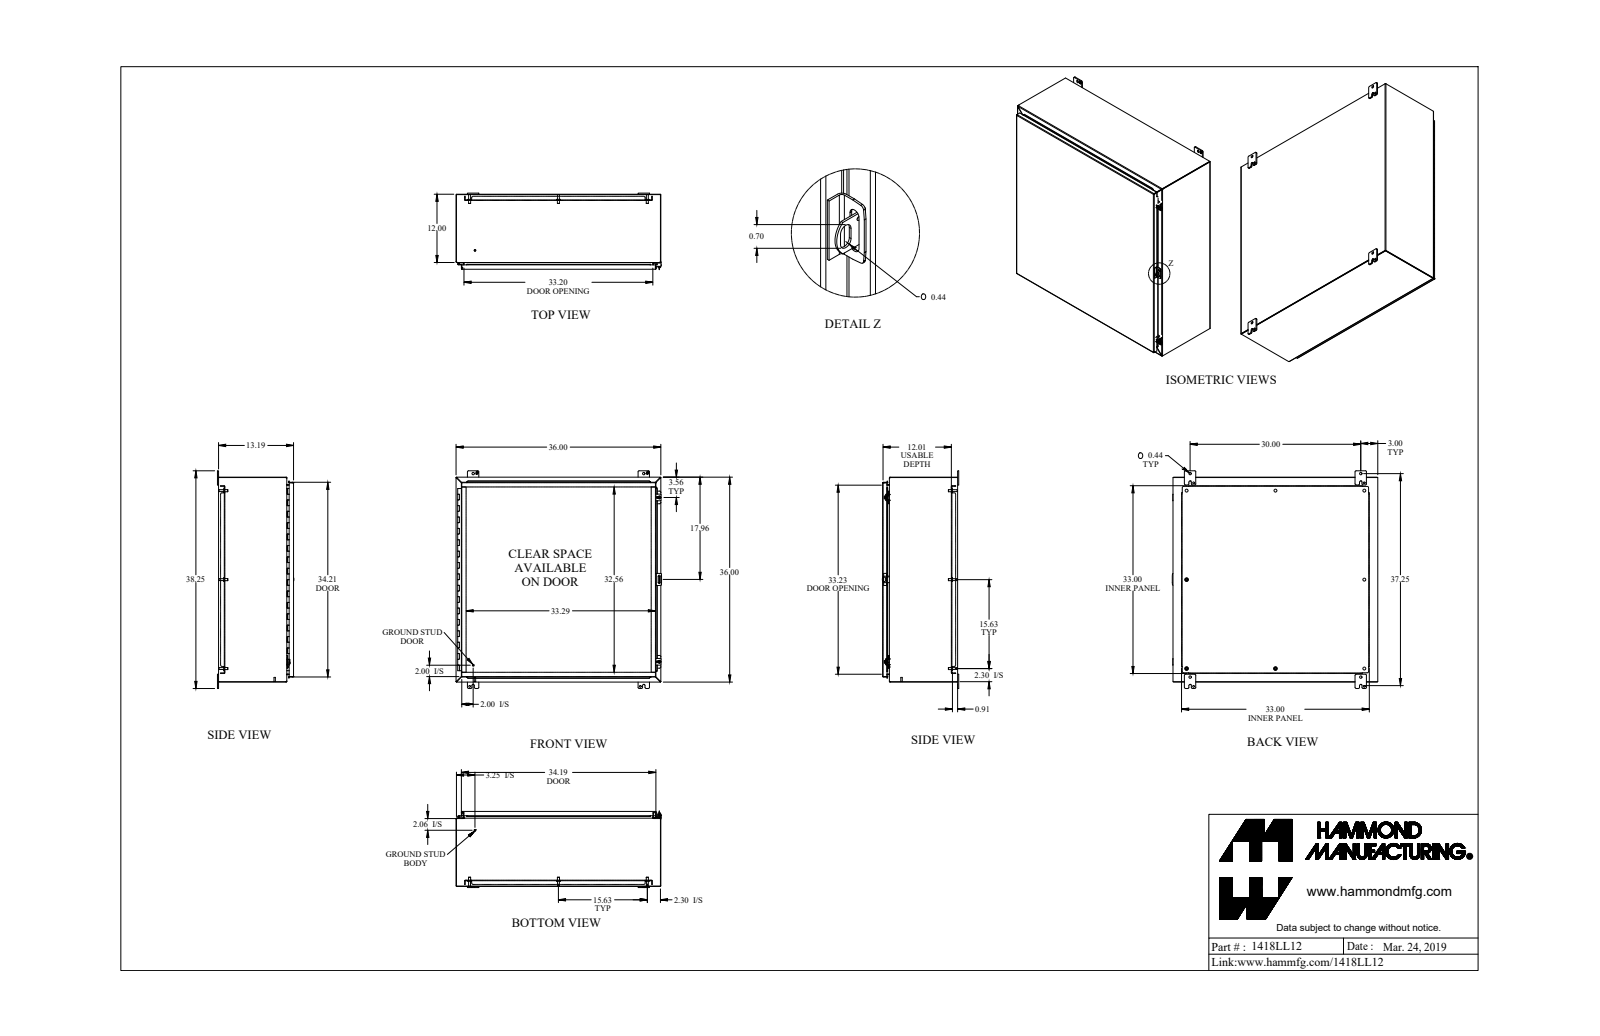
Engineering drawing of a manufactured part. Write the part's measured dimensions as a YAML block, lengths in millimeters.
part_name: "1418LL12_Default"
step_written_by: "SolidWorks 2019 (CONFIG_CONTROL_DESIGN)"
units: millimeters
bodies: {solids: 52, faces: 1493, planar: 859, cylindrical: 526, other: 108}
overall_size: [971.6, 917.6, 341.3]
volume: 8194000
surface_area: 8401000
round_holes:
  - {diameter: 12.7, count: 8}
  - {diameter: 7.8, count: 4}
  - {diameter: 8, count: 4}
  - {diameter: 11.1, count: 4}
  - {diameter: 11.3, count: 4}
  - {diameter: 5.4, count: 2}
  - {diameter: 6.7, count: 2}
  - {diameter: 9.5, count: 2}
  - {diameter: 3.2, count: 1}
  - {diameter: 4.7, count: 1}
round_bosses_or_shafts:
  - {diameter: 16.5, count: 8}
  - {diameter: 9.5, count: 8}
  - {diameter: 8.4, count: 8}
  - {diameter: 25.4, count: 4}
  - {diameter: 12.7, count: 2}
  - {diameter: 9.9, count: 2}
  - {diameter: 7.1, count: 2}
  - {diameter: 6.4, count: 2}
partial_cylinders:
  - {radius: 4.8, count: 40}
  - {radius: 0.9, count: 22}
  - {radius: 2.7, count: 22}
  - {radius: 6.4, count: 20}
  - {radius: 2.9, count: 16}
  - {radius: 1.2, count: 13}
  - {radius: 3.6, count: 13}
  - {radius: 1, count: 8}
face_to_face_distances: [1.8, 333.1, 912.6, 331.2, 334.9, 2.4, 23.8, 25.6, 306.9, 305]
hole_center_spacings: [396.9, 887.5, 793.8, 793.8, 396.9, 762, 887.5, 61.8]
